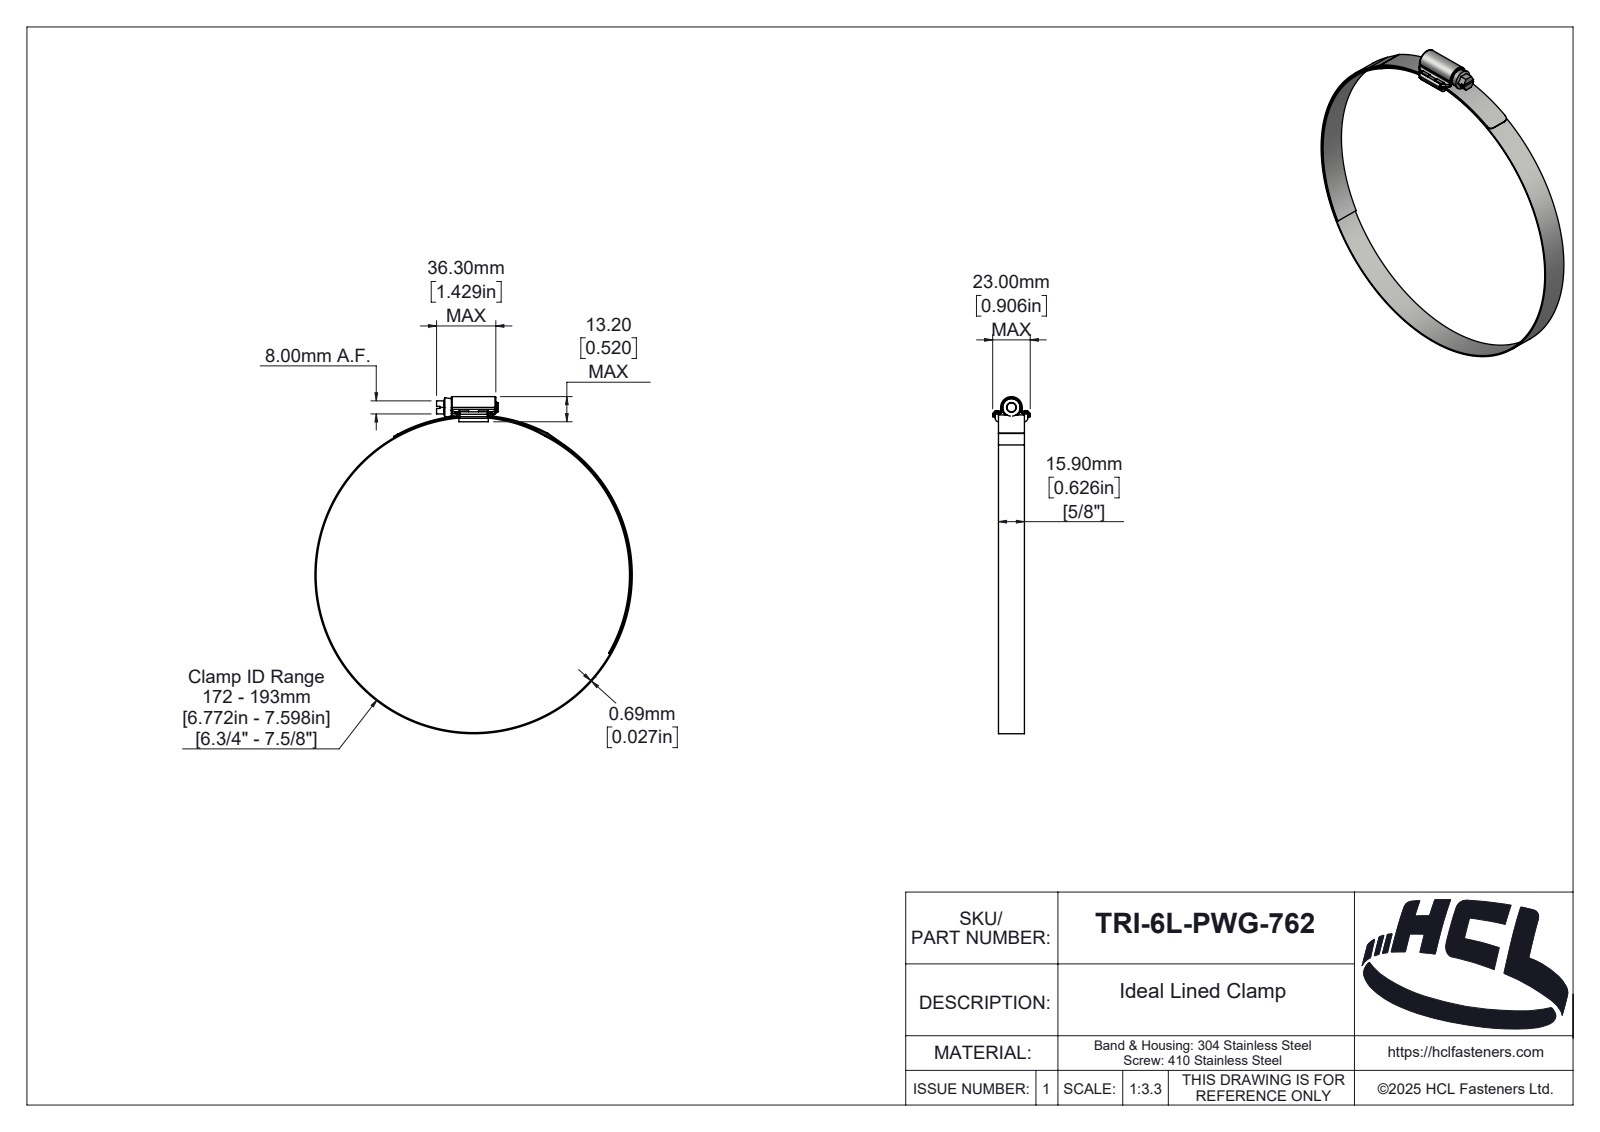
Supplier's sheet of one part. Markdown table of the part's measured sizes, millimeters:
| quantity | value |
| --- | --- |
| part name | TRI-6L-PWG-762 |
| STEP written by | SolidWorks 2025 (AUTOMOTIVE_DESIGN) |
| units | millimeters |
| bodies | 4 solids, 268 faces (87 planar, 102 cylindrical, 79 other) |
| overall size | 206.39 × 194.38 × 23 |
| volume | 14 639 mm³ |
| surface area | 33 173 mm² |
| round holes (diameter × count) | 193 × 1 |
| round bosses / shafts (diameter × count) | 194.38 × 1, 10.7 × 1, 6 × 1 |
| partial cylindrical surfaces (radius × count) | 1 × 14, 0.5 × 4, 1.5 × 4, 2 × 3, 0.1 × 2, 2.1 × 2, 3 × 2, 0.46 × 1 |
| main face-to-face distances | 15.9, 2, 0.69, 17.9, 4.9, 1.2, 4.55, 3.35, 15.35, 2.55 |
